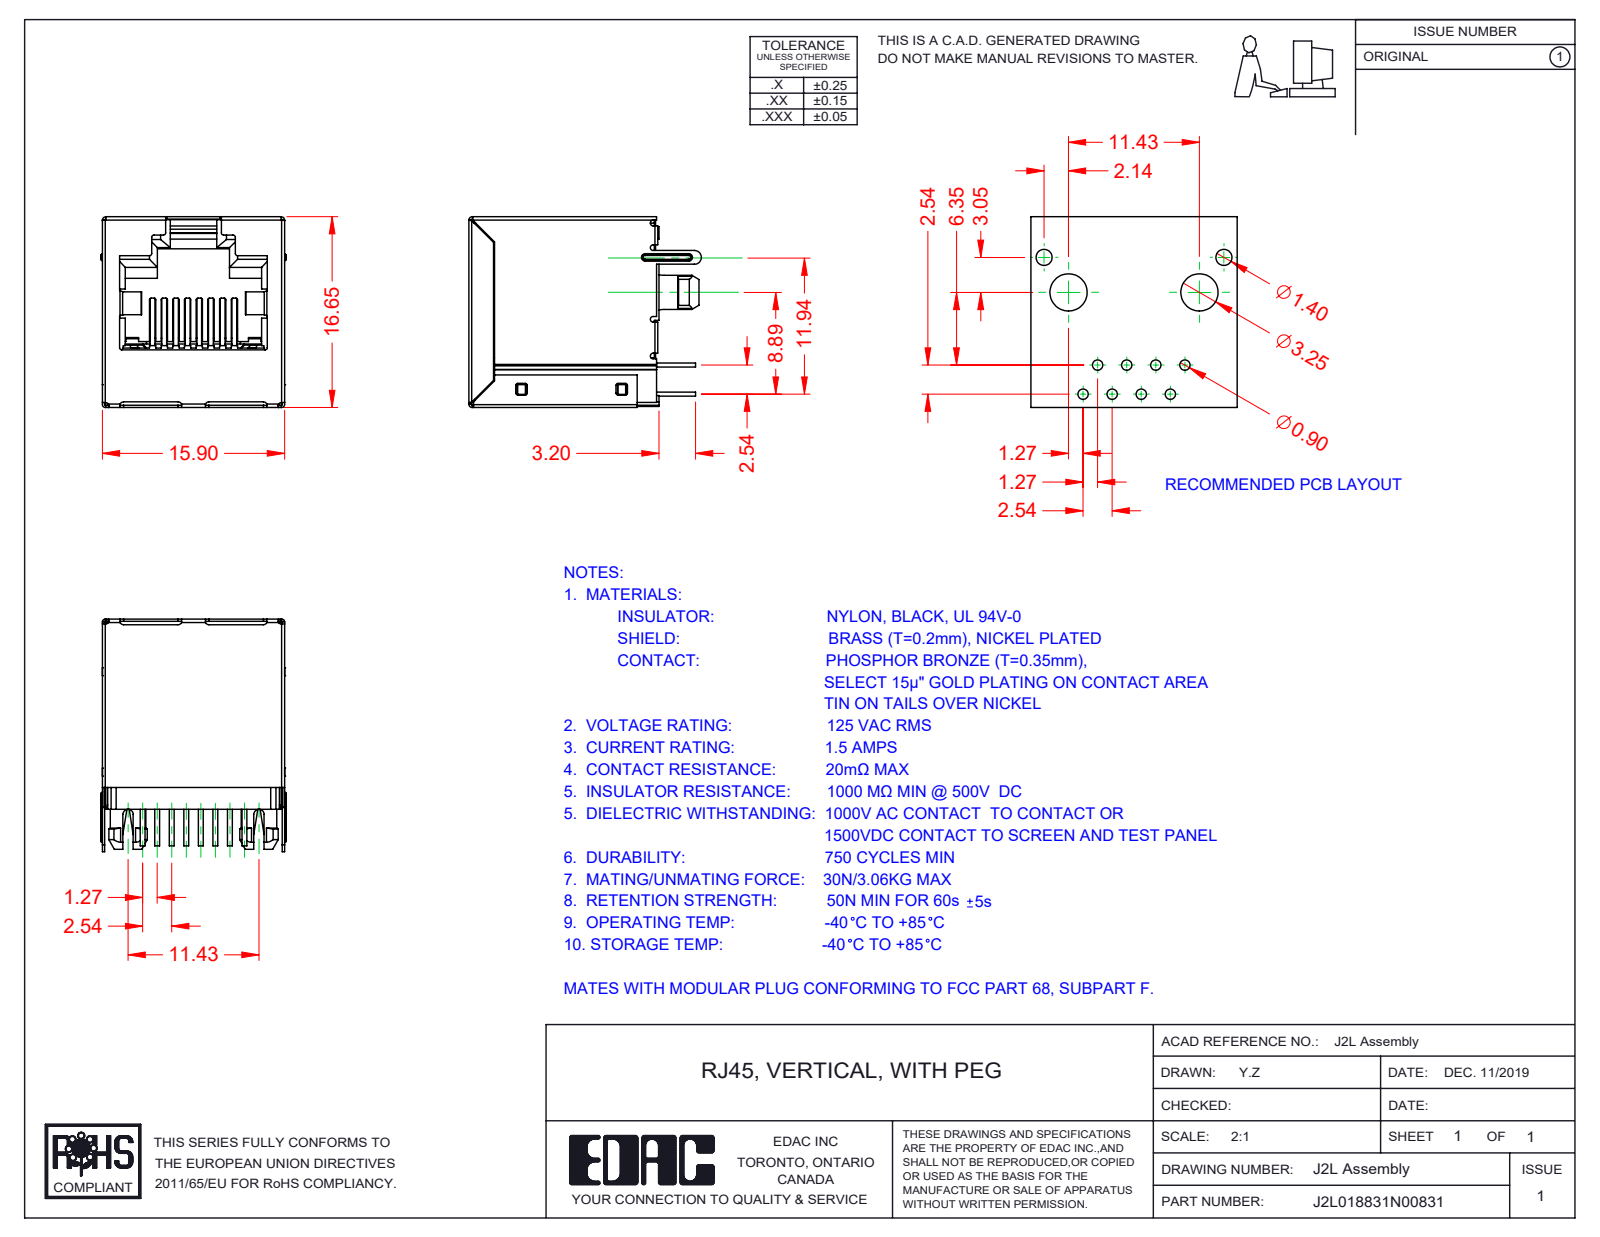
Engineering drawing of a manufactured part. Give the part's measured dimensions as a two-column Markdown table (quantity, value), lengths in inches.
| quantity | value |
| --- | --- |
| part name | 2L Contact Lock; RJ2L018831N00831; 2L Mylar Tape; 2L Insulator (+2 more) |
| STEP written by | SolidWorks 2016 (CONFIG_CONTROL_DESIGN) |
| units | inches |
| bodies | 12 solids, 1131 faces (784 planar, 284 cylindrical, 63 other) |
| overall size | 0.799 × 0.656 × 0.638 |
| volume | 0.167 in³ |
| surface area | 10.61 in² |
| round bosses / shafts (diameter × count) | 0.122 × 2, 0.043 × 2 |
| partial cylindrical surfaces (radius × count) | 0.006 × 64, 0.01 × 20, 0.008 × 16, 0.012 × 14, 0.014 × 9, 0.004 × 8, 0.011 × 4, 0.02 × 3 |
| main face-to-face distances | 0.608, 0.618, 0.648, 0.638, 0.646, 0.616, 0.642, 0.64, 0.626, 0.61 |
